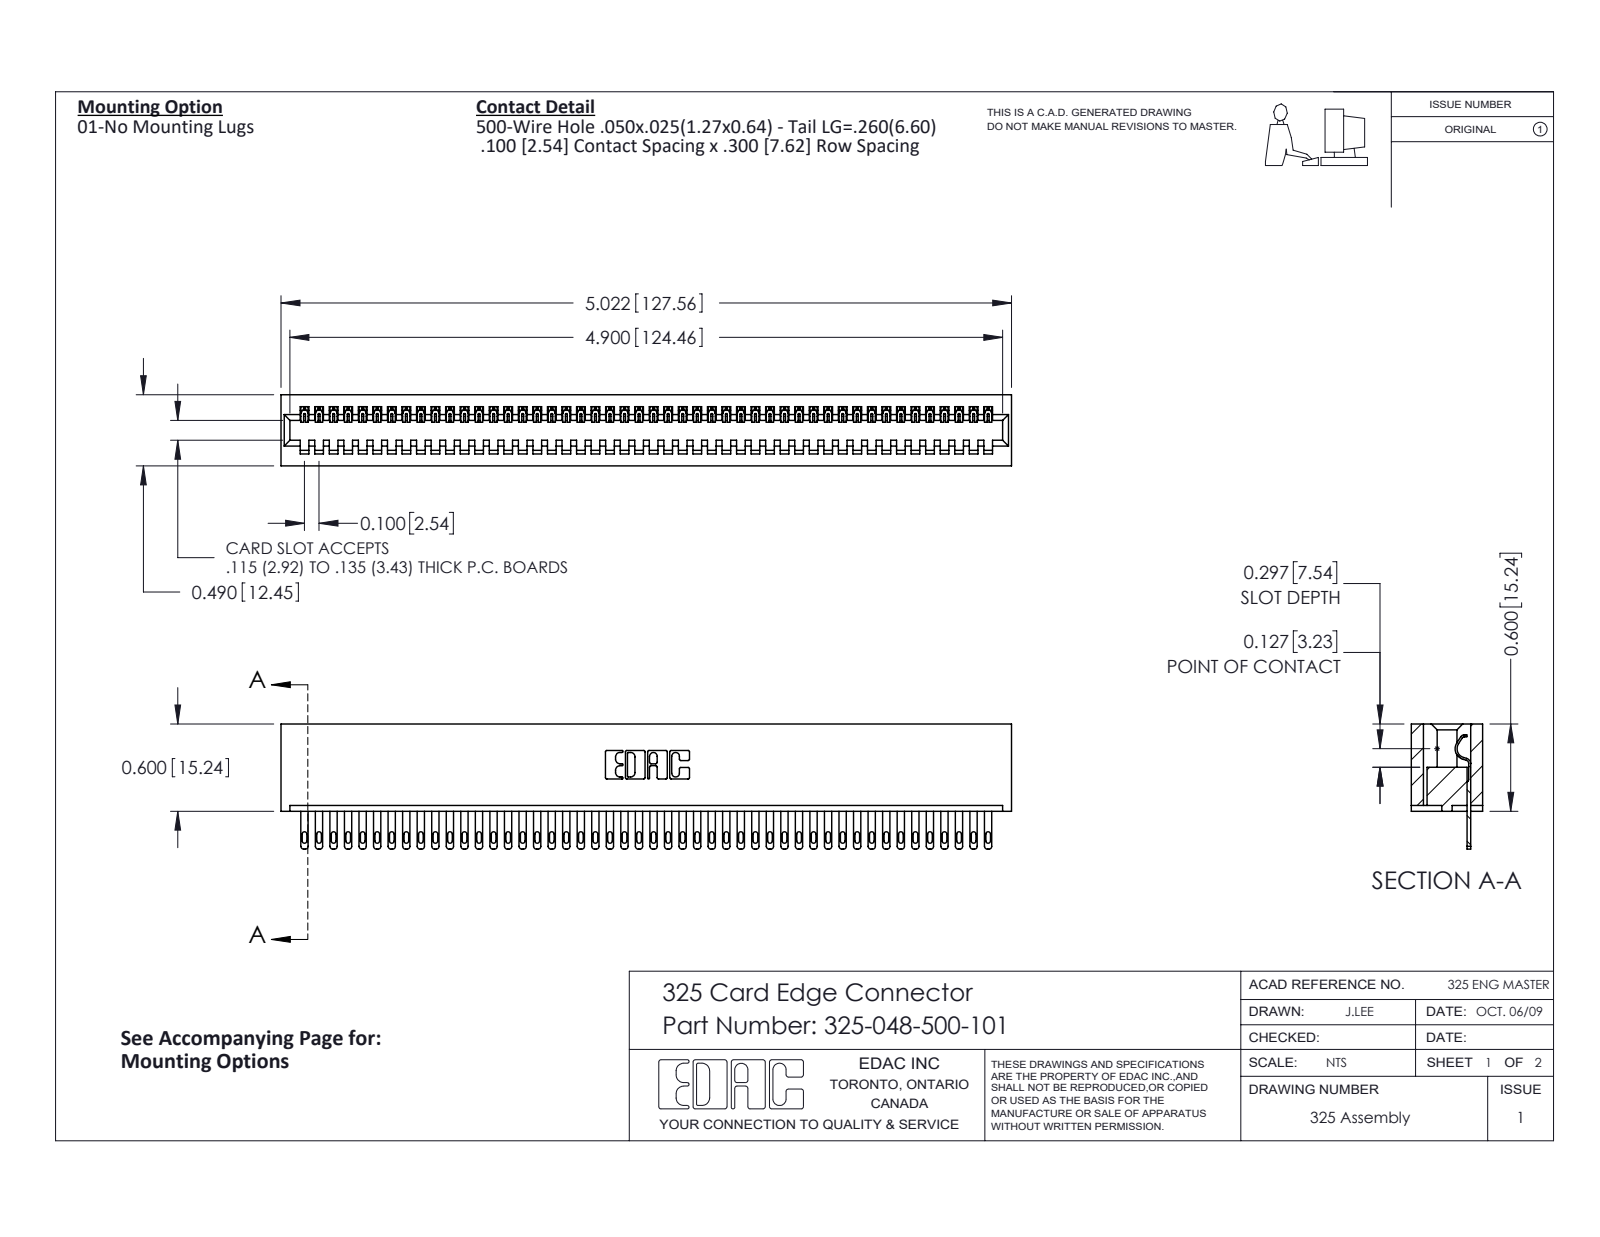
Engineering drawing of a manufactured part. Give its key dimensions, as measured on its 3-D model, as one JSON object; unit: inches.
{"part_name": "325-048-500-101; 325-292-001_325-293-100; 325 Part_Lugless", "step_written_by": "SolidWorks 2016 (CONFIG_CONTROL_DESIGN)", "units": "inches", "bodies": {"solids": 49, "faces": 2698, "planar": 1794, "cylindrical": 904, "other": 0}, "overall_size": [5.022, 0.86, 0.49], "volume_in3": 1.028, "surface_area_in2": 29.61, "partial_cylinders_radius": [[0.006, 96], [0.016, 96], [0.02, 96], [0.01, 22], [0.007, 6], [0.031, 6], [0.026, 3], [0.014, 1]], "face_to_face_distances": [0.083, 0.407, 0.49, 0.3, 0.107, 0.383, 0.025, 0.325, 0.56, 0.263]}
